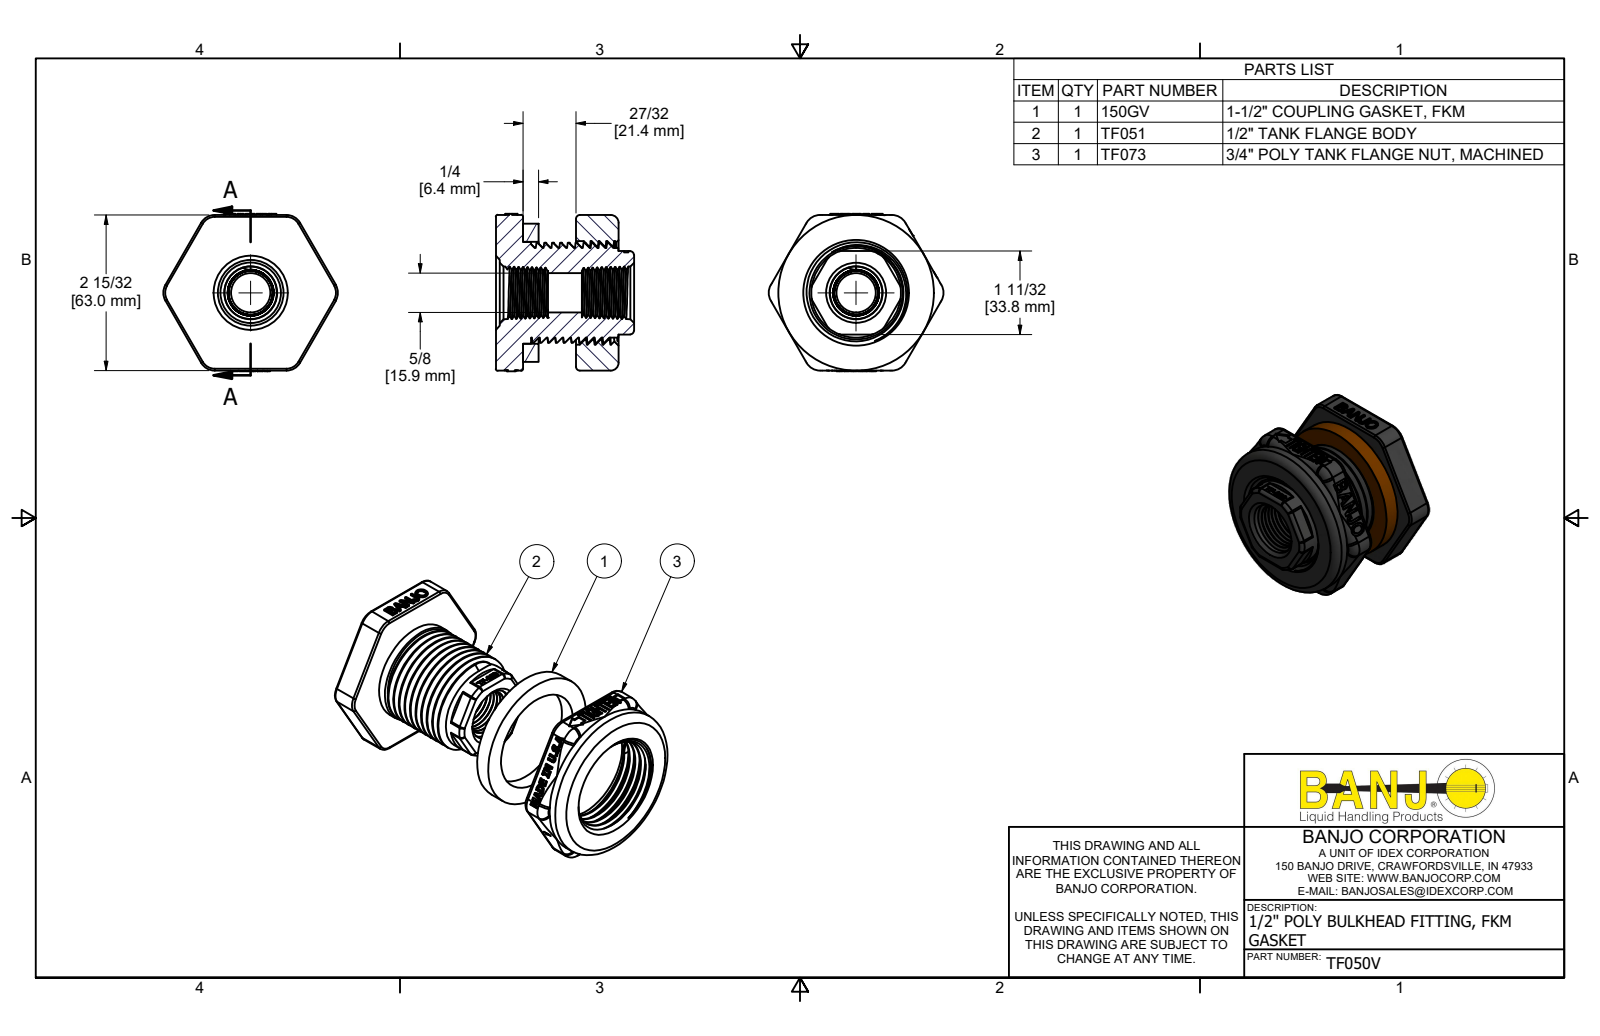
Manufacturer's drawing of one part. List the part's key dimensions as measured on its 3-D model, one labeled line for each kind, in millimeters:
Part name (STEP PRODUCT): TF050V; TF051; TF073; TF073X (+1 more)
STEP written by: Autodesk Inventor 2022 (AUTOMOTIVE_DESIGN)
Units: millimetres
Bodies: 3 solids, 870 faces (491 planar, 102 cylindrical, 277 other)
Overall size (bounding box): 70.8 × 63.8 × 55.9
Volume: 113 600 mm³ · Surface area: 37 170 mm²
Round holes (diameter × count): ⌀15.9 ×1, ⌀37.7 ×1, ⌀41.3 ×1, ⌀41.9 ×1
Round bosses / shafts (diameter × count): ⌀63 ×1, ⌀55.9 ×1, ⌀41.1 ×1, ⌀40.5 ×1, ⌀36.3 ×1
Partial cylindrical surfaces — rounded edges, fillets, slot ends (radius × count): R1.5 ×18, R0.8 ×12, R1.6 ×6, R3.2 ×6, R6.4 ×6, R6.6 ×1, R11.2 ×1, R12.6 ×1
Main face-to-face distances: 10.9, 32.4, 21.4, 6.4, 17.3, 15.1, 32.4, 63, 49.6, 38.7
